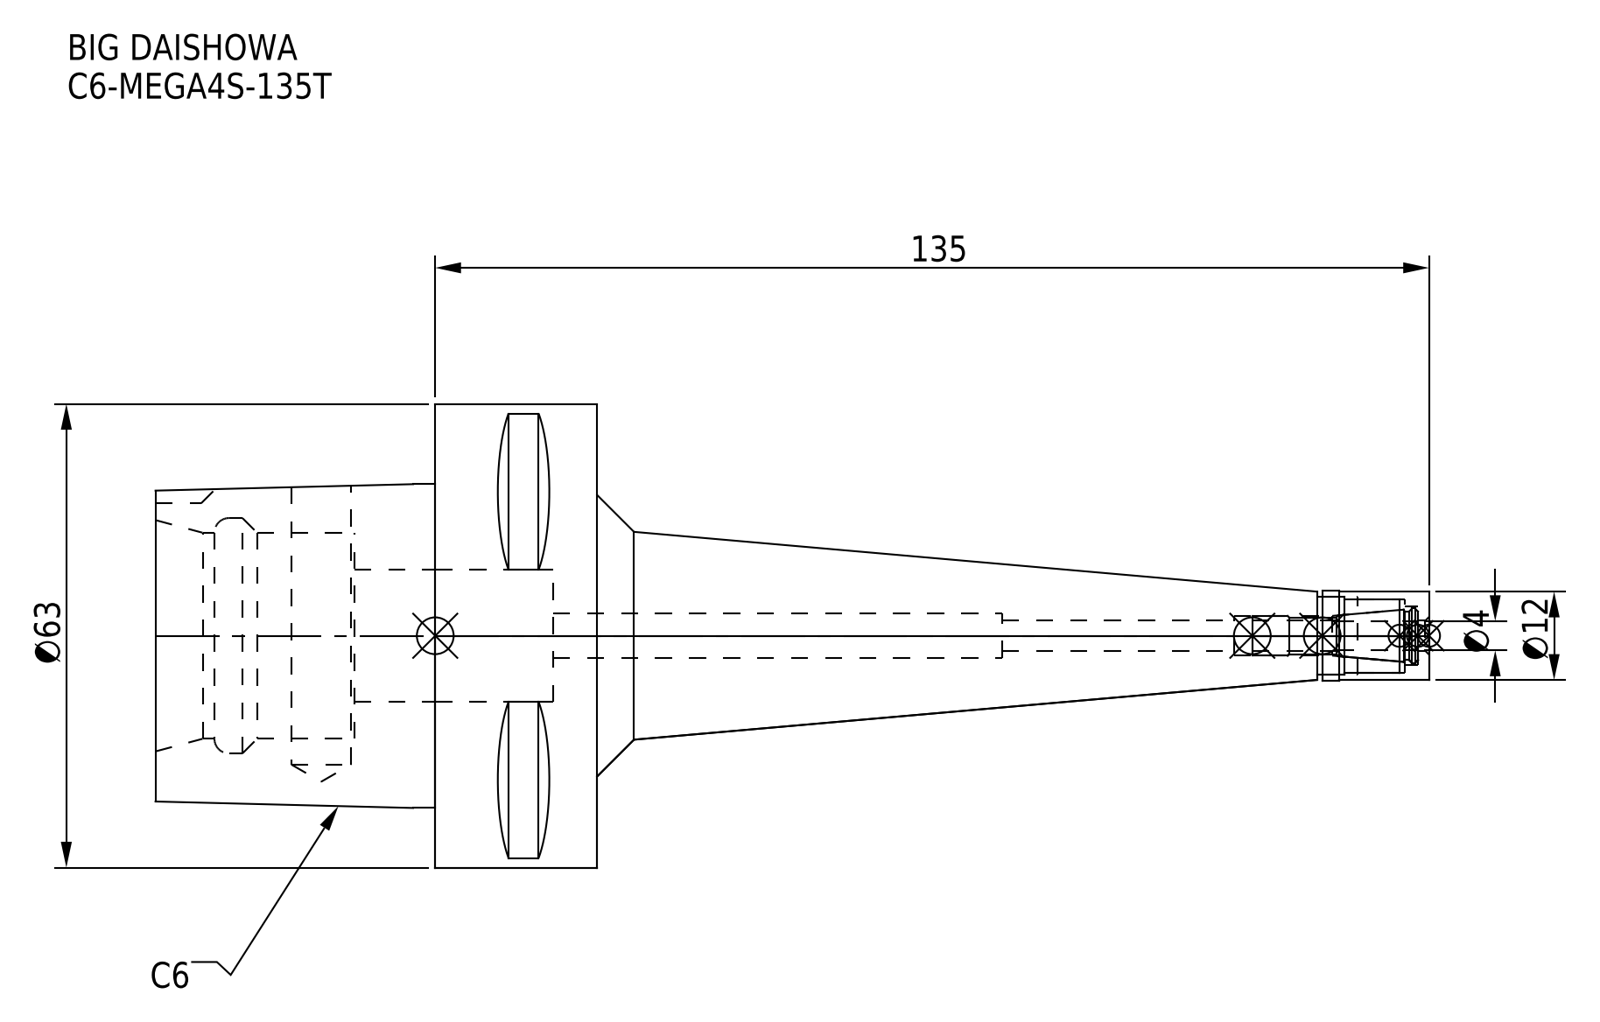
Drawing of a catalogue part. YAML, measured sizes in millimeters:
part_name: "DXF_TEMP_ASSY_ASM_4_ASM.stp; C6-MEGA4S-135T-040_ASM.stp; C6-MEGA4S-135T-040.stp; C6-MEGA4S-135T_1.stp (+3 more)"
step_written_by: "SolidWorks 2019 (CONFIG_CONTROL_DESIGN)"
units: millimeters
bodies: {solids: 2, faces: 93, planar: 38, cylindrical: 37, other: 18}
overall_size: [173, 63, 63]
volume: 130848
surface_area: 29198
round_holes:
  - {diameter: 4.1, count: 1}
  - {diameter: 4.2, count: 1}
  - {diameter: 5.4, count: 1}
  - {diameter: 6, count: 1}
  - {diameter: 8, count: 1}
  - {diameter: 8.1, count: 1}
  - {diameter: 10, count: 1}
  - {diameter: 10.5, count: 1}
  - {diameter: 18, count: 1}
  - {diameter: 28, count: 1}
  - {diameter: 32, count: 1}
round_bosses_or_shafts:
  - {diameter: 63, count: 1}
  - {diameter: 12.3, count: 1}
  - {diameter: 12, count: 1}
partial_cylinders:
  - {radius: 5, count: 1}
face_to_face_distances: [22, 27, 60, 38, 33, 11, 24.89, 55.4, 54, 6]
